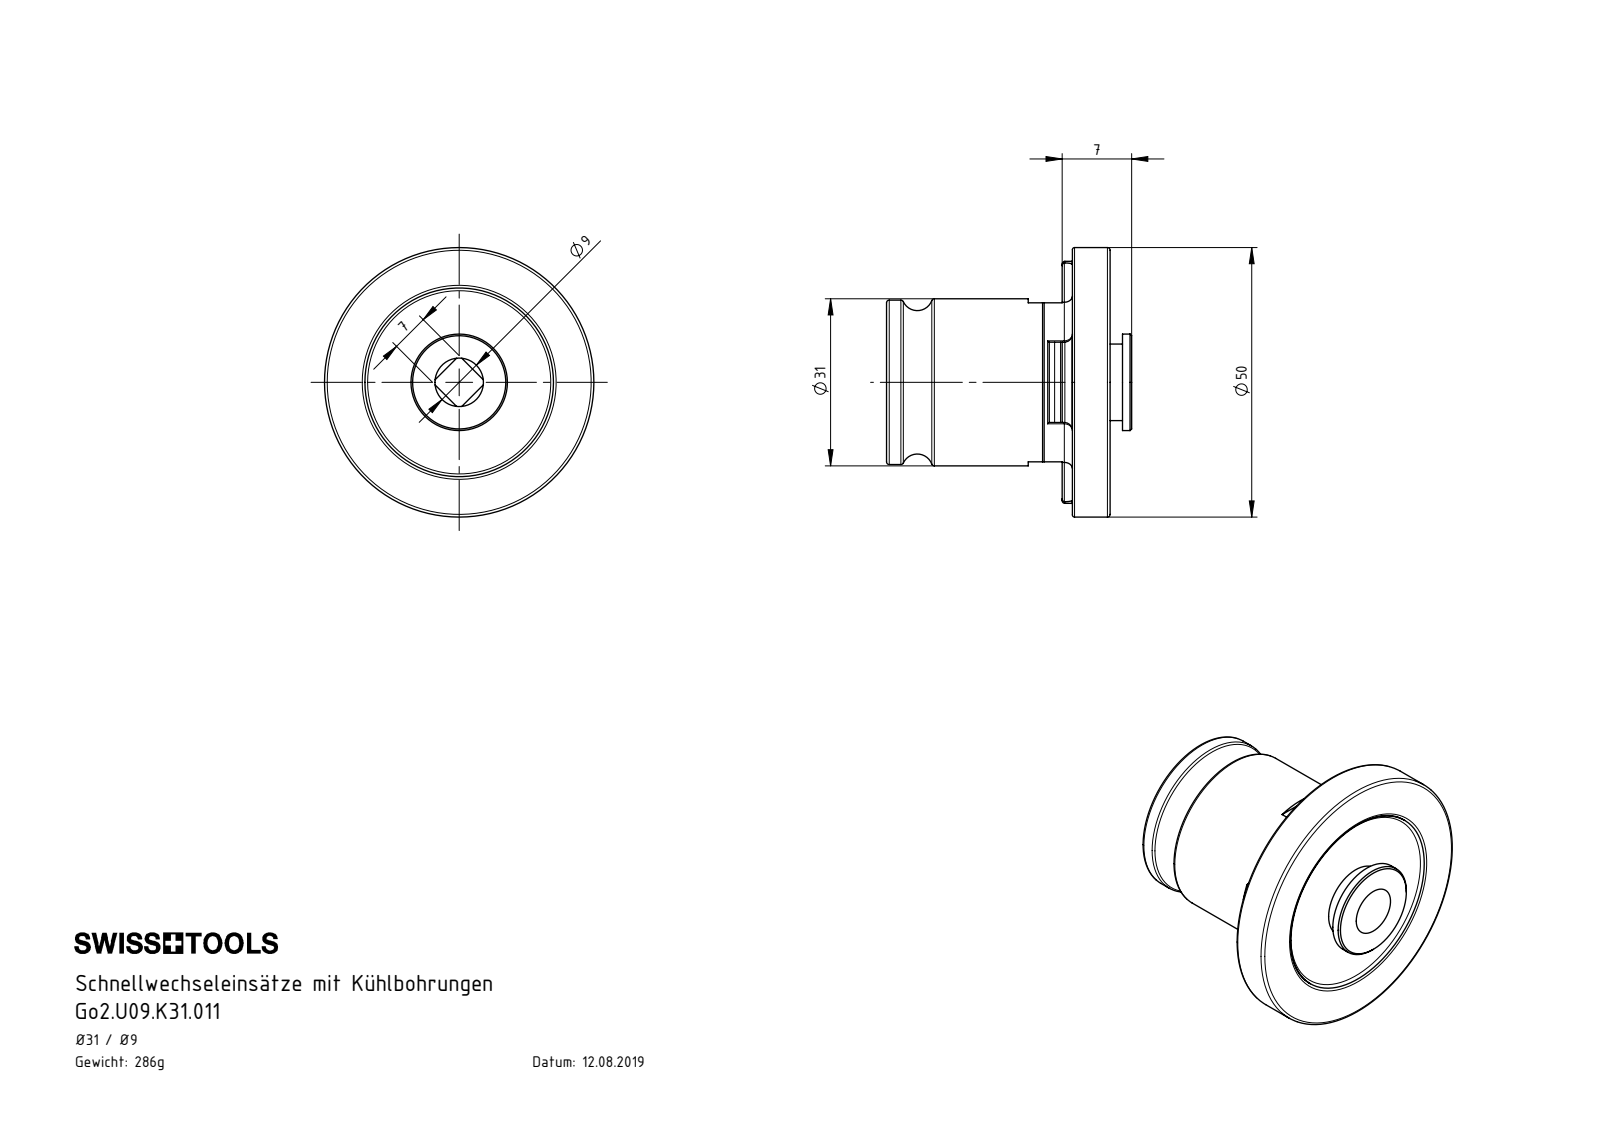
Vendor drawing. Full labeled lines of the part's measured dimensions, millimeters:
Part name (STEP PRODUCT): Go2.U09.K31.011
STEP written by: SolidWorks 2017 (AUTOMOTIVE_DESIGN)
Units: millimetres
Bodies: 1 solid, 102 faces (37 planar, 28 cylindrical, 37 other)
Overall size (bounding box): 50 × 50 × 45.5
Volume: 36 395 mm³ · Surface area: 10 236 mm²
Round holes (diameter × count): ⌀9 ×1, ⌀20.1 ×1
Round bosses / shafts (diameter × count): ⌀50 ×1, ⌀35 ×1, ⌀31 ×1, ⌀30.6 ×1, ⌀30.5 ×1, ⌀17.9 ×1, ⌀14.2 ×1
Partial cylindrical surfaces — rounded edges, fillets, slot ends (radius × count): R1.5 ×5, R0.5 ×4, R20 ×1, R22.45 ×1
Main face-to-face distances: 7, 0.65, 6.35, 34.5, 40.85, 41.5, 3, 31.5, 37.85, 38.5
